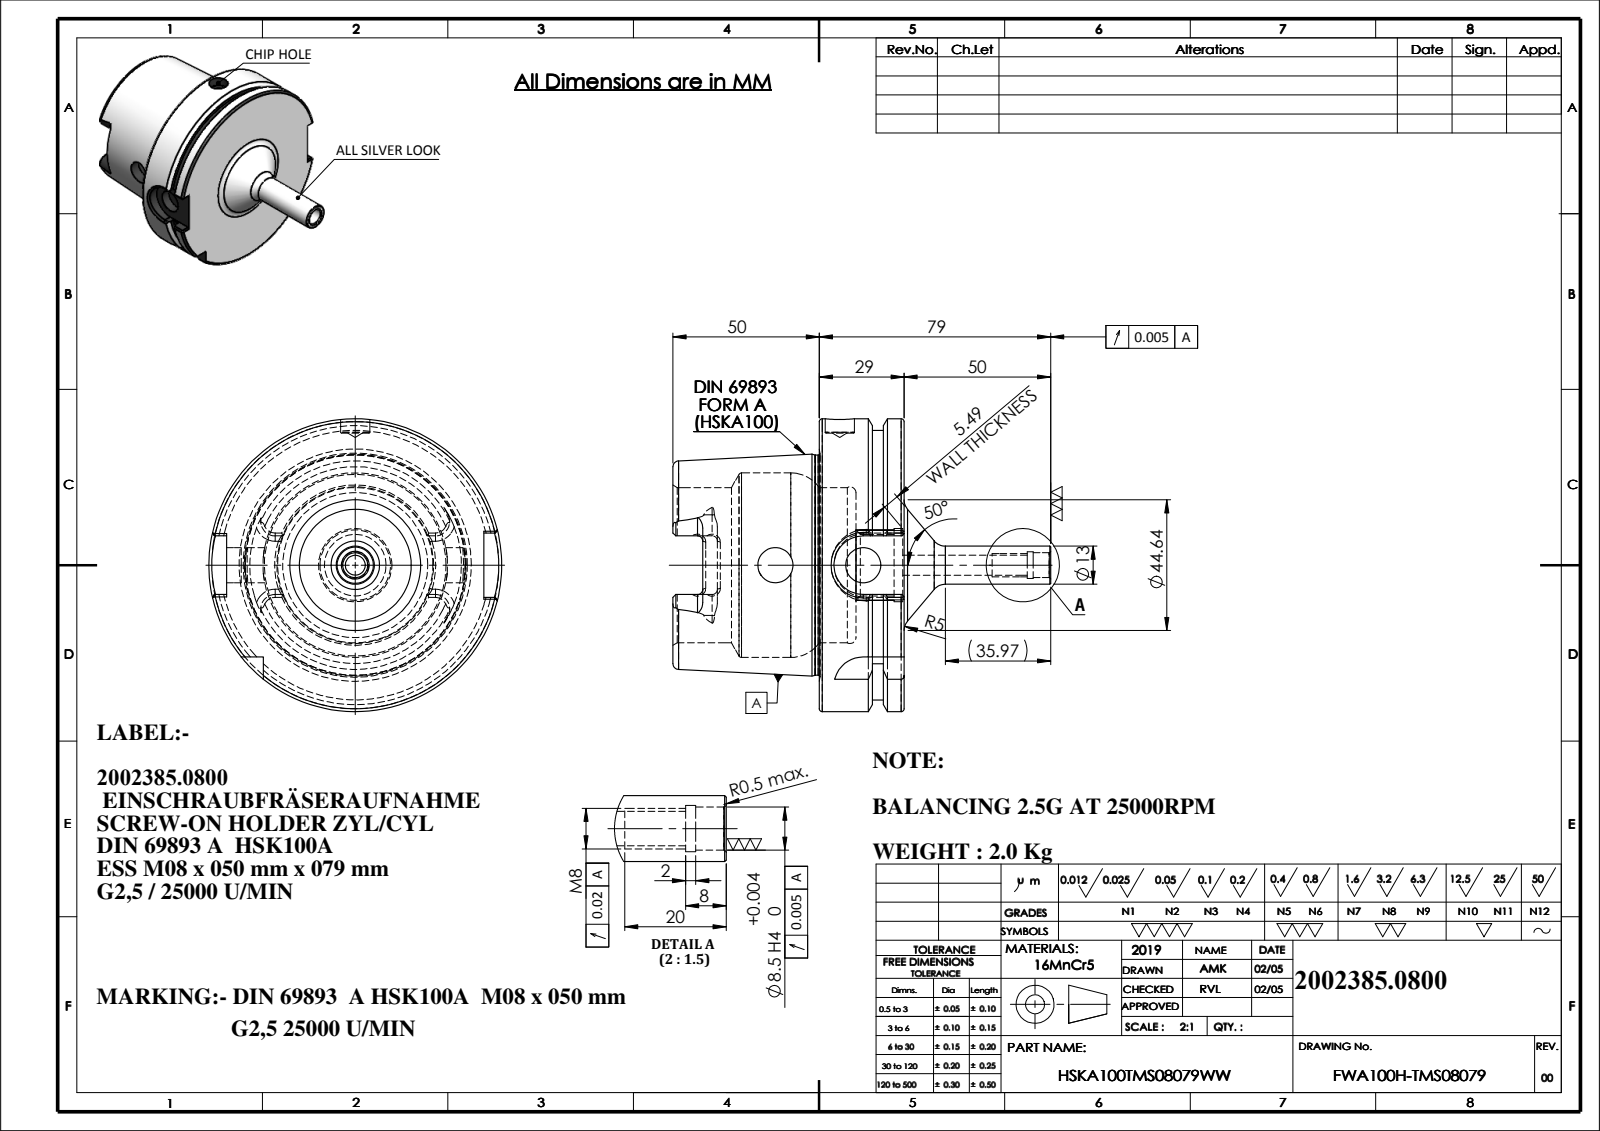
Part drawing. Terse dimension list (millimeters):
name: 91100A-EZ8M08050
written by: SolidWorks 2018 (CONFIG_CONTROL_DESIGN)
unit: mm
bodies: 1 solid, 174 faces (50 planar, 52 cylindrical, 72 other)
size: 129 × 100 × 100
volume: 264 204 mm³; area: 52 814 mm²
holes: 2× ⌀12, 1× ⌀6.8, 1× ⌀8.5, 1× ⌀9.1, 1× ⌀10, 1× ⌀21, 1× ⌀25, 1× ⌀53, 1× ⌀63
bosses: 1× ⌀100, 1× ⌀92, 1× ⌀75.16, 1× ⌀13
rounds: 6× R1.8, 4× R4.88, 2× R10, 1× R11
face distances: 28.95, 12.5, 16.45, 50, 62.5, 78.95, 78.5, 28.5, 16, 0.45
hole spacings: 30
